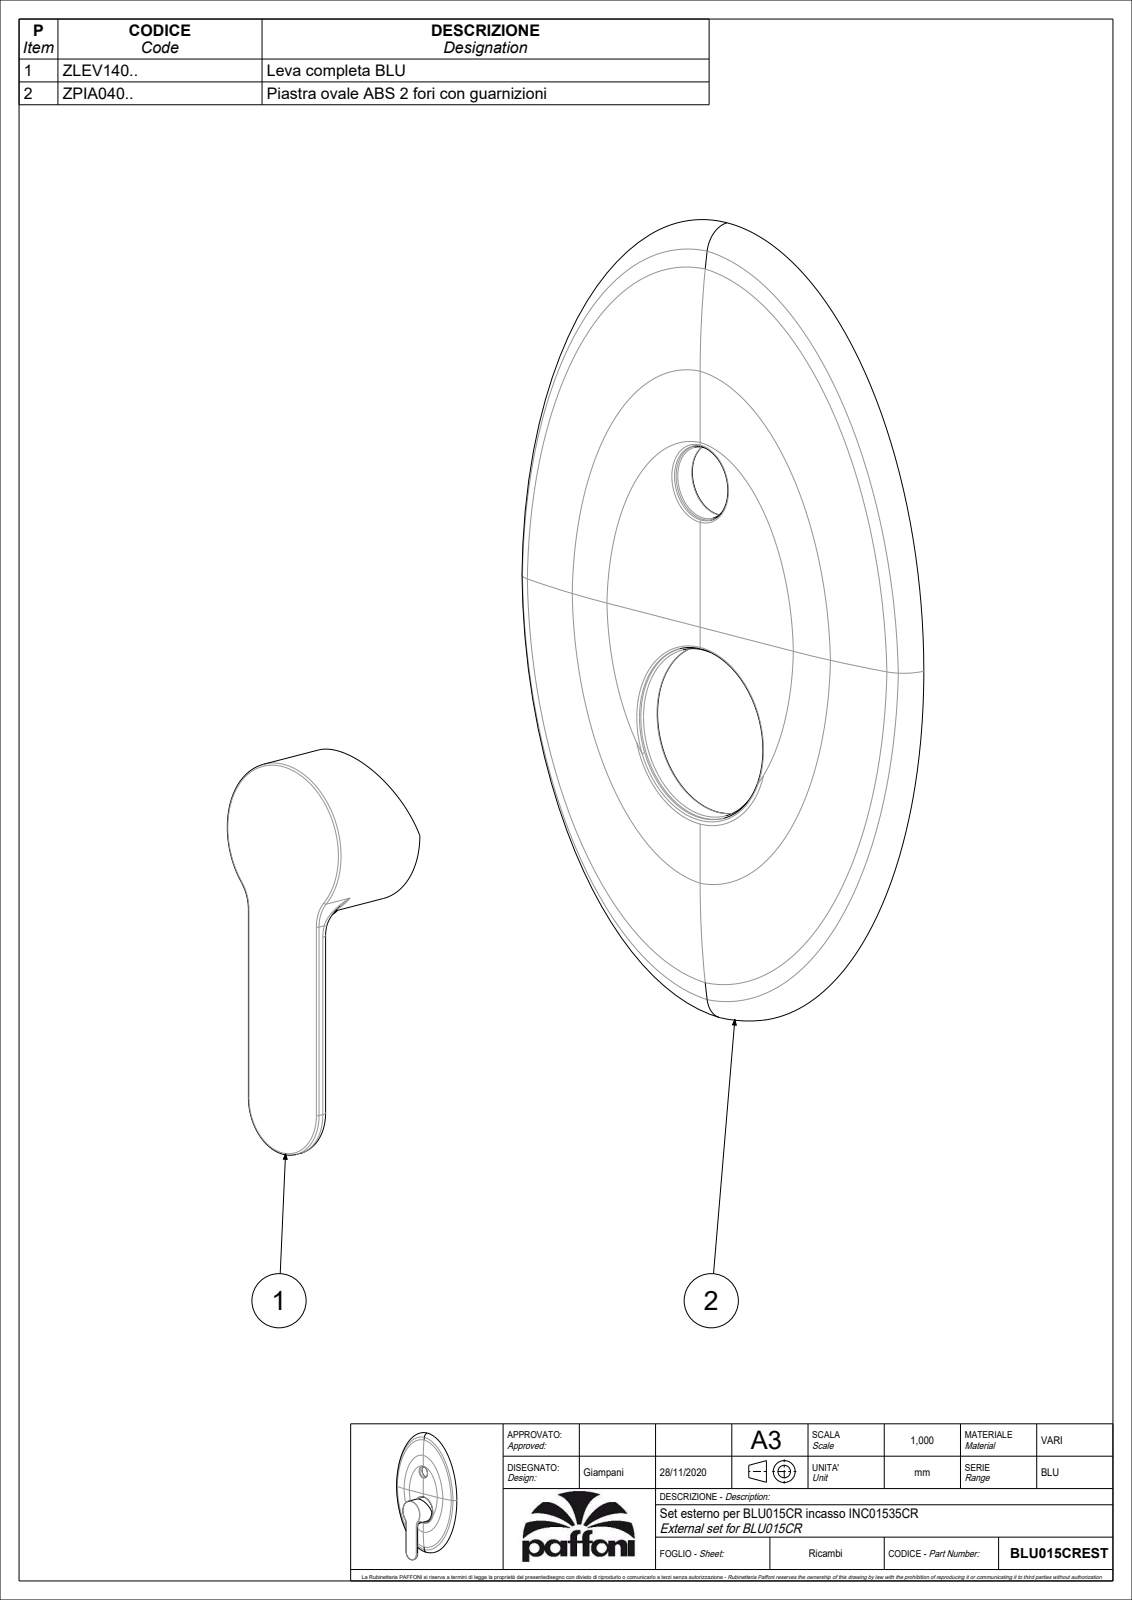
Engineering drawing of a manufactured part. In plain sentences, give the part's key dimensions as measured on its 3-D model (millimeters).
The part is named "BLU015CREST". Its 3-D file was written by "CREO PARAMETRIC BY PTC INC, 2020044 (CONFIG_CONTROL_DESIGN)". It is 2 solids with 239 faces: 61 planar, 70 cylindrical and 108 other. Overall it measures 222 by 146 by 40.34 millimeters. Its volume is 81 203 cubic millimeters and its surface area 67 012 square millimeters. Round holes: 1 of diameter 3, 1 of diameter 3.3, 1 of diameter 4.5, 1 of diameter 19.2, 1 of diameter 20, 1 of diameter 23.2, 1 of diameter 45, 1 of diameter 46. Round bosses or shafts: 1 of diameter 51, 1 of diameter 49, 1 of diameter 42, 1 of diameter 25, 1 of diameter 23, 1 of diameter 7.6, 1 of diameter 5.5, 1 of diameter 5. Partial cylindrical surfaces (rounded edges, fillets, slot ends): 8 of radius 1.2, 7 of radius 1, 2 of radius 0.5, 2 of radius 1.6, 2 of radius 2.5, 2 of radius 10, 1 of radius 13, 1 of radius 800. The main face-to-face distances are 35.5, 1, 36.5, 3, 32.5, 33.5, 0.5, 10, 9.1, 26. The hole center spacings are 68.
